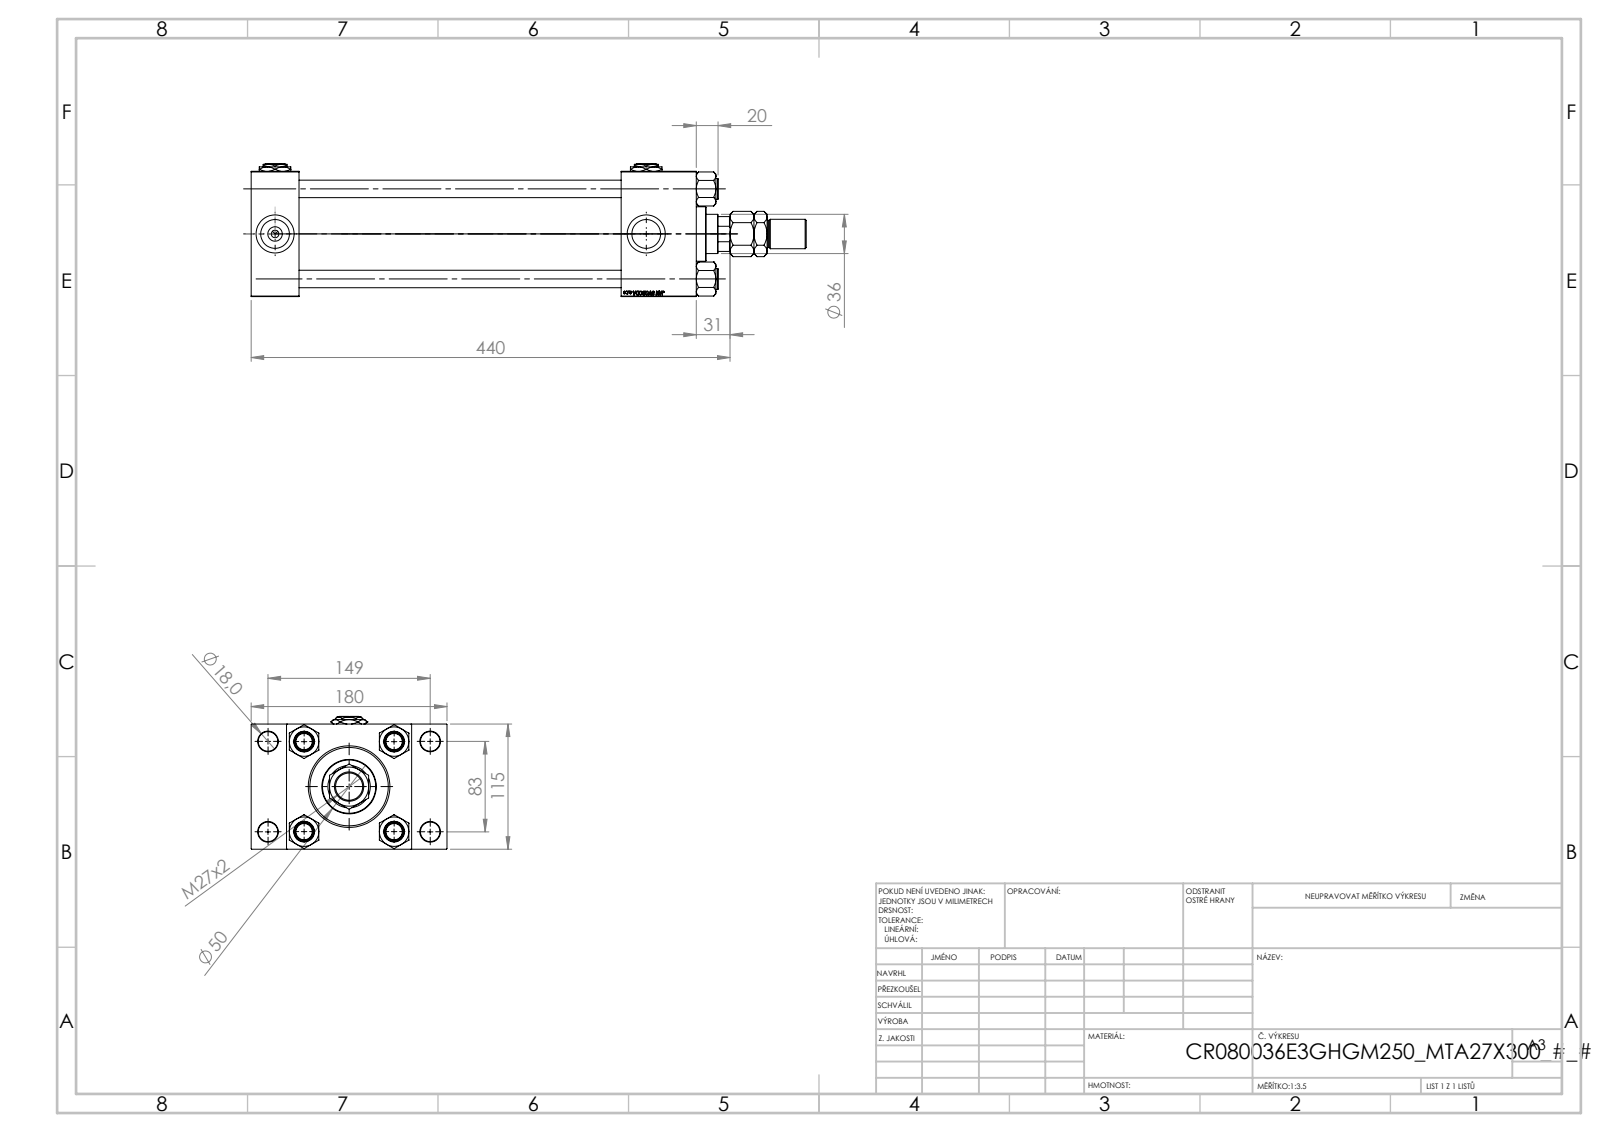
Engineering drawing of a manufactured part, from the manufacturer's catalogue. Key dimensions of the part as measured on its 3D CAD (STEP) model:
Part name (STEP PRODUCT): MTA; NUT_M5_E; V215CR_VCP_E; V215CR_E_Body (+3 more)
STEP written by: SolidWorks 2019 (CONFIG_CONTROL_DESIGN)
Units: millimetres
Bodies: 14 solids, 1339 faces (610 planar, 105 cylindrical, 624 other)
Overall size (bounding box): 510 × 180 × 122
Volume: 2 727 000 mm³ · Surface area: 519 044 mm²
Round holes (diameter × count): ⌀16 ×4, ⌀18 ×4, ⌀26.44 ×4, ⌀35 ×4, ⌀7 ×3, ⌀2.5 ×2, ⌀25.5 ×1, ⌀36 ×1, ⌀39 ×1, ⌀61 ×1, ⌀72 ×1, ⌀80 ×1
Round bosses / shafts (diameter × count): ⌀19 ×4, ⌀86 ×1, ⌀50 ×1, ⌀27 ×1, ⌀25 ×1
Partial cylindrical surfaces — rounded edges, fillets, slot ends (radius × count): R17.5 ×1
Main face-to-face distances: 115, 44, 409, 365, 32.5, 147.5, 69, 340, 296, 380.3
Hole centre spacings: 33.15, 41.96, 57.81, 58.48, 82.7, 85.28, 86.17, 89.24
